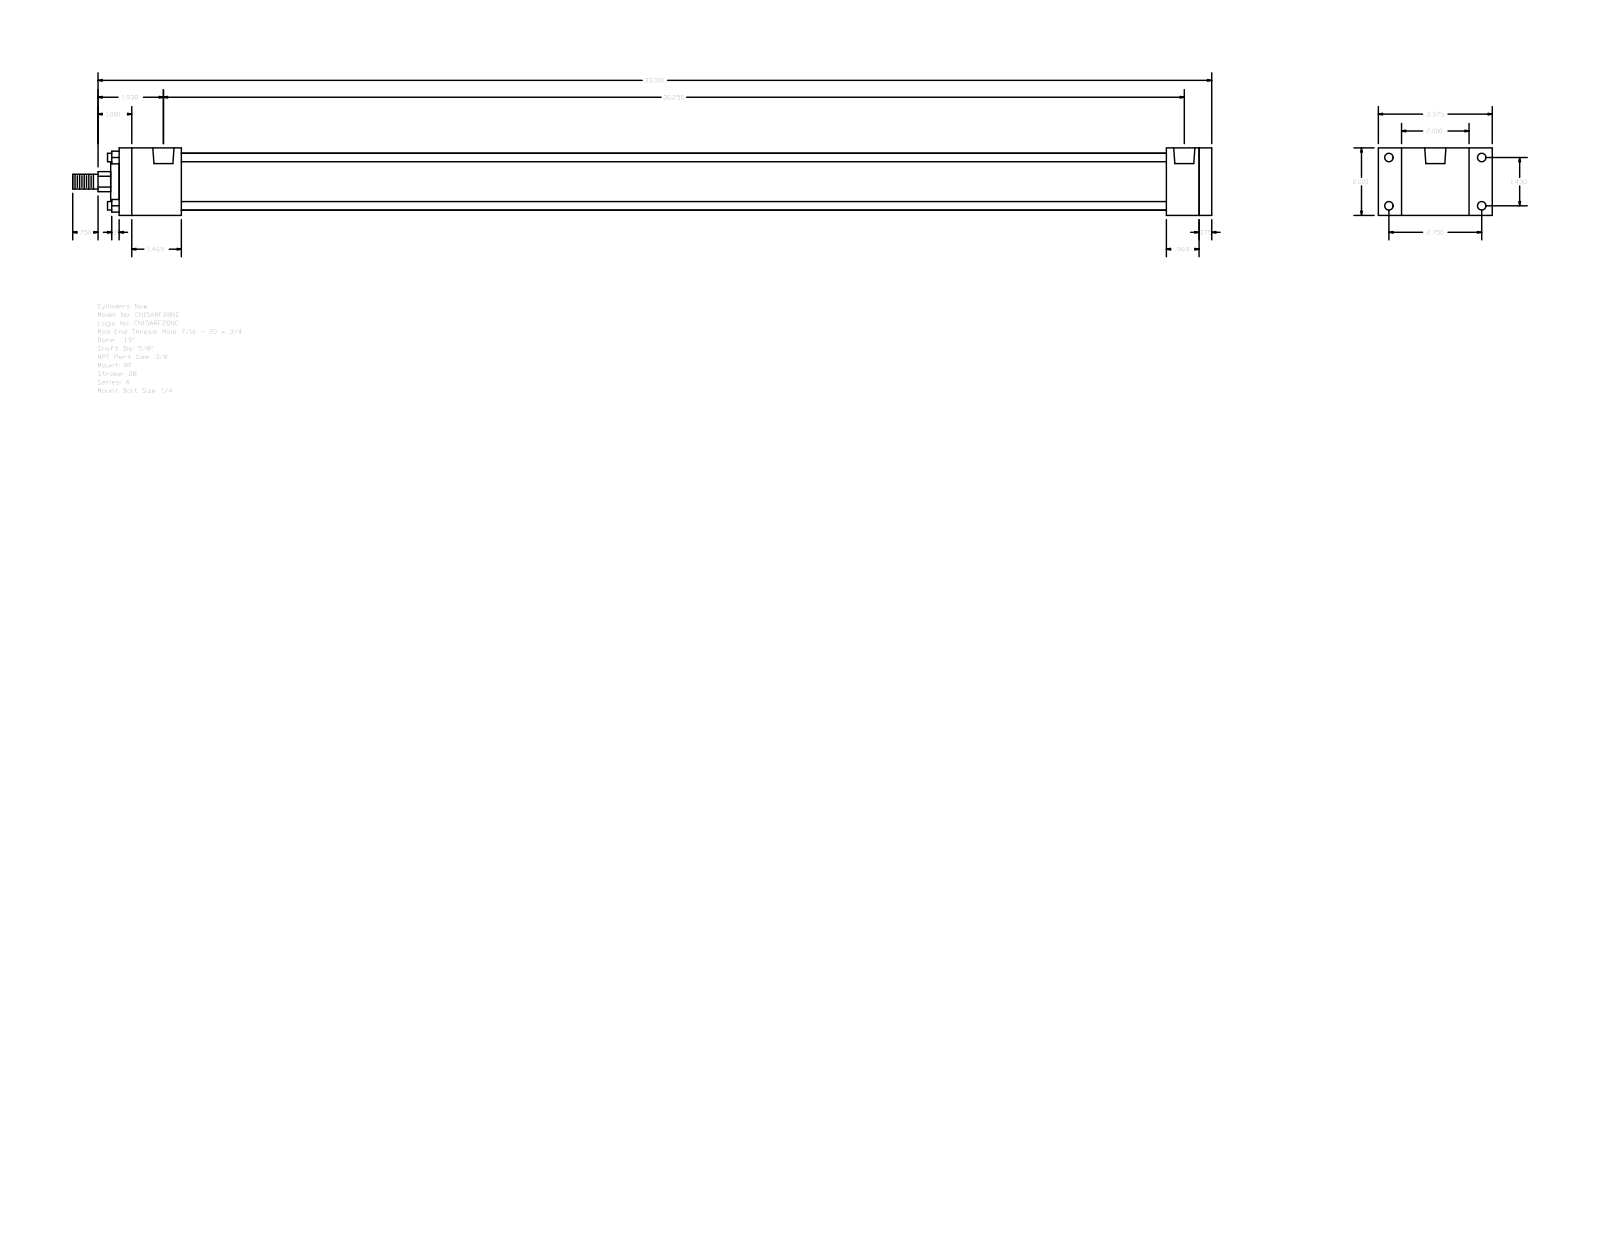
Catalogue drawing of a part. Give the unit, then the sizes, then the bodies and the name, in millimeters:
Units: millimetres
Overall size (bounding box): 857.25 × 85.72 × 50.8
Round holes (diameter × count): ⌀5.56 ×4, ⌀6.35 ×4, ⌀15.93 ×2
Round bosses / shafts (diameter × count): ⌀6.35 ×4, ⌀42.93 ×1, ⌀28.57 ×1, ⌀15.88 ×1, ⌀11.11 ×1
Partial cylindrical surfaces — rounded edges, fillets, slot ends (radius × count): R7.54 ×1
Main face-to-face distances: 50.8, 9.53, 822.32, 812.79, 788.19, 24.6, 34.13, 46.83, 741.36, 765.96
Hole centre spacings: 3.97, 36.32, 69.84, 78.72, 760.41, 764.38, 768.35
Bodies: 0 solids, 92 faces (64 planar, 28 cylindrical, 0 other)
Part name (STEP PRODUCT): A_RF__0150_0.625
STEP written by: GSSL Pune (CONFIG_CONTROL_DESIGN)
